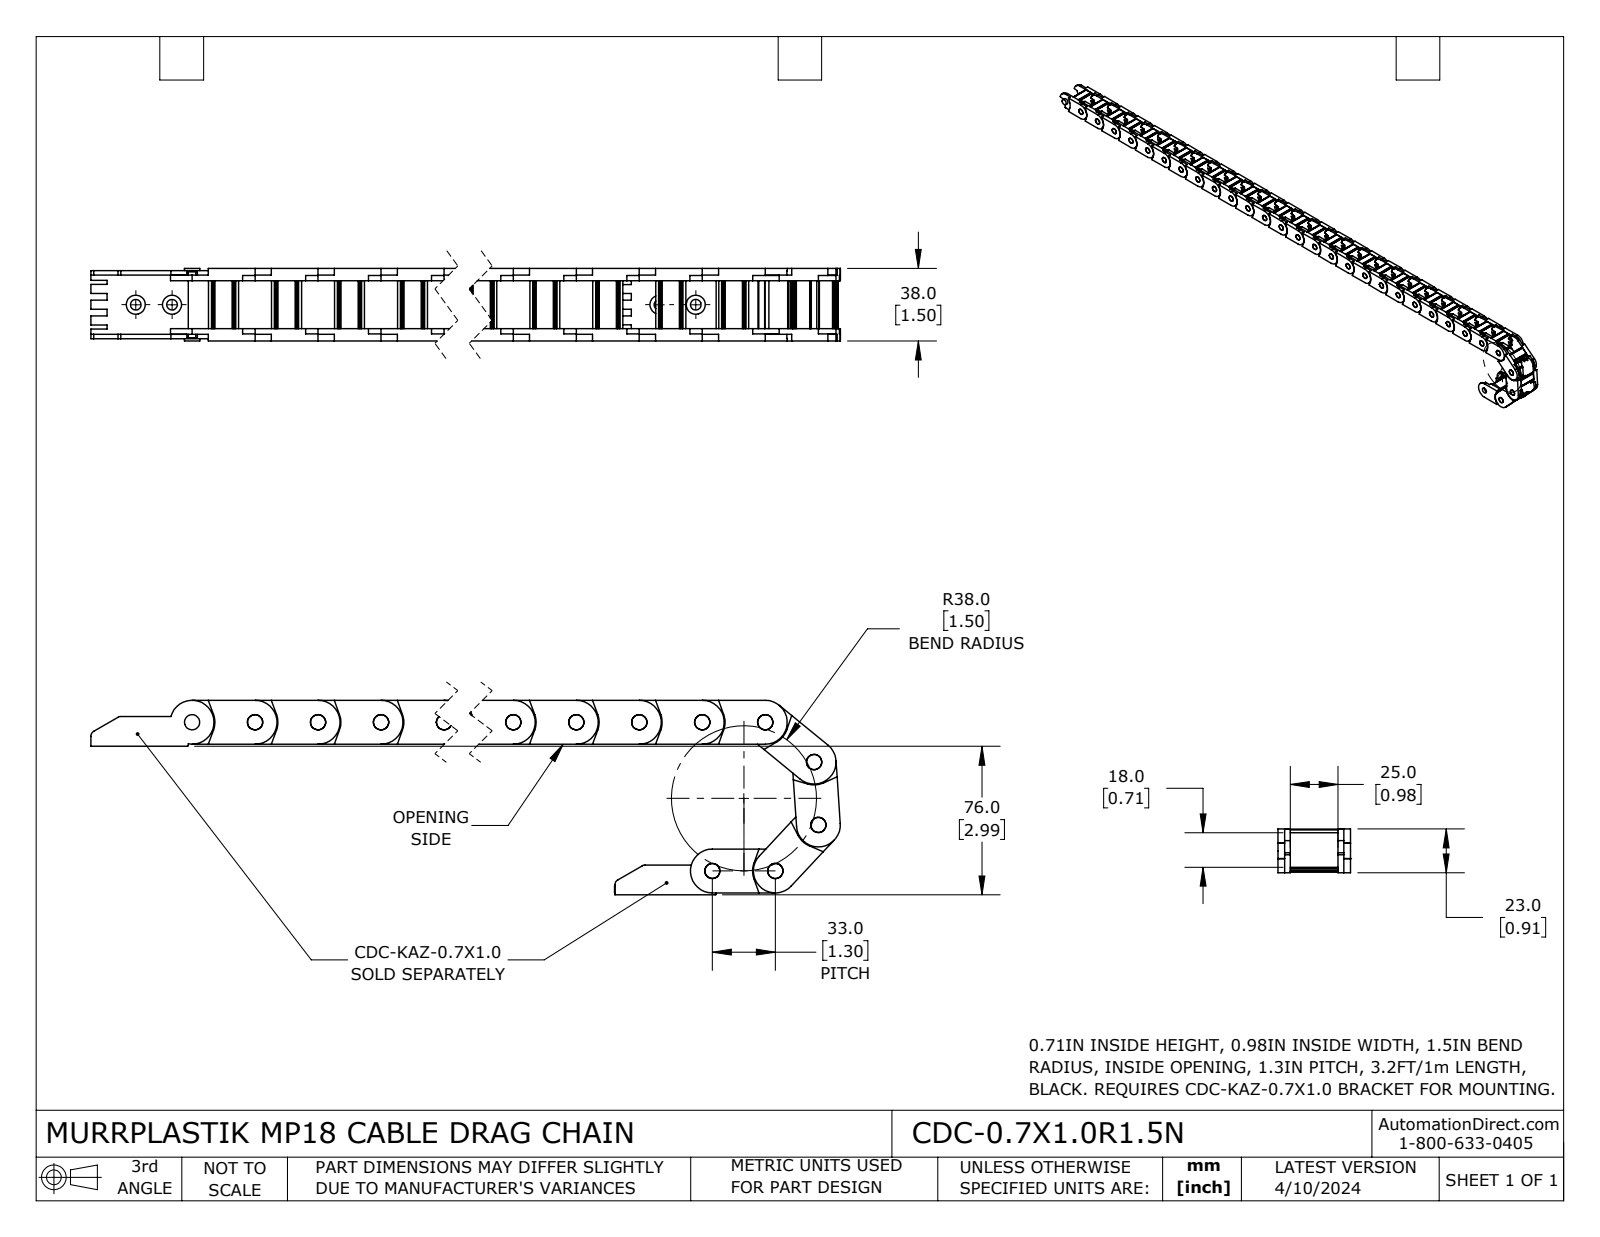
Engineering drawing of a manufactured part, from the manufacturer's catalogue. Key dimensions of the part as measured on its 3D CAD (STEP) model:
Part name (STEP PRODUCT): CDC-0.7X1.0R1.5N
STEP written by: SolidWorks 2023 (CONFIG_CONTROL_DESIGN)
Units: millimetres
Bodies: 30 solids, 2550 faces (1290 planar, 1260 cylindrical, 0 other)
Overall size (bounding box): 908.64 × 100.88 × 38
Volume: 307 300 mm³ · Surface area: 223 840 mm²
Round holes (diameter × count): ⌀8 ×30
Round bosses / shafts (diameter × count): ⌀8 ×1
Partial cylindrical surfaces — rounded edges, fillets, slot ends (radius × count): R0.5 ×120, R1.5 ×120, R0.2 ×60, R0.3 ×60, R11.5 ×31, R11.95 ×31, R5 ×30, R5.45 ×30
Main face-to-face distances: 6.5, 31.5, 38, 3.5, 34.5, 3, 28, 25, 3.7, 34.3
Hole centre spacings: 33, 66, 99, 132, 165, 198, 231, 264
